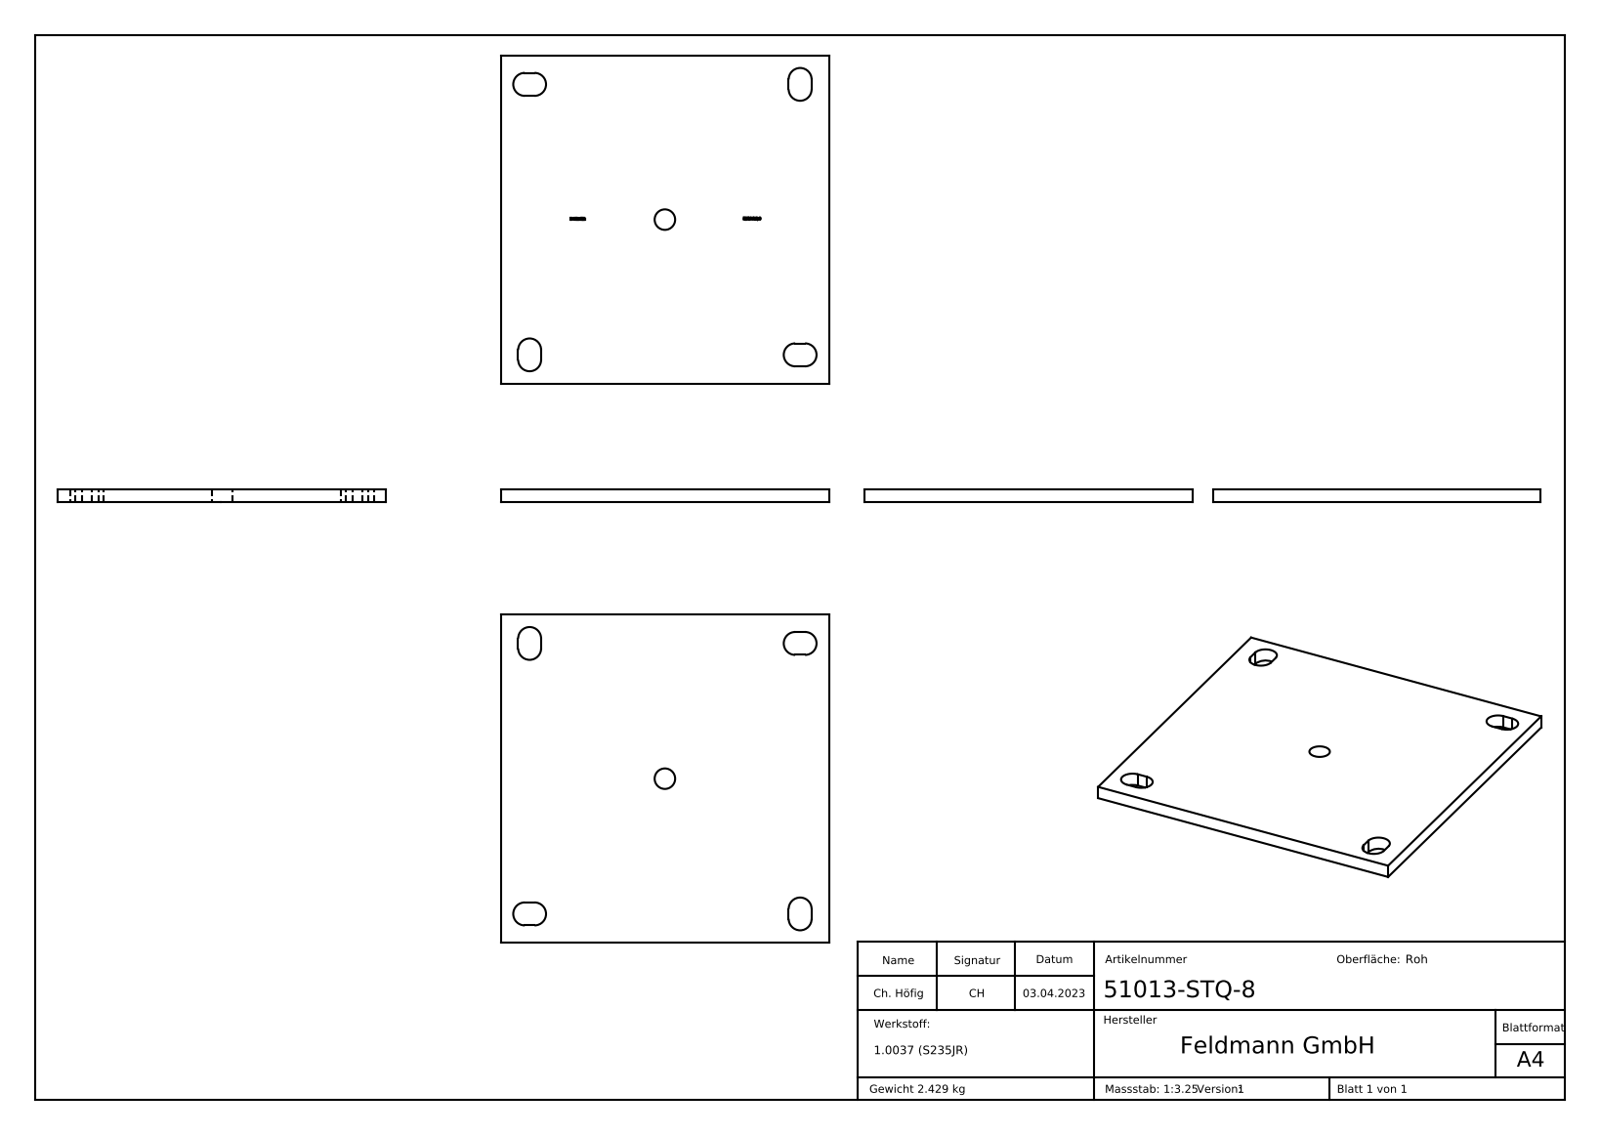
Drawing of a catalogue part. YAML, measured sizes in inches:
part_name: "51013-STQ-8"
step_written_by: "SolidWorks 2018 (CONFIG_CONTROL_DESIGN)"
units: inches
bodies: {solids: 1, faces: 269, planar: 139, cylindrical: 9, other: 121}
overall_size: [7.874, 7.874, 0.315]
volume: 19
surface_area: 133.9
round_holes:
  - {diameter: 0.492, count: 1}
partial_cylinders:
  - {radius: 0.276, count: 8}
face_to_face_distances: [0.315, 7.874, 0.413, 0.965, 6.909, 7.461, 0.551, 6.496, 7.047, 5.945]
